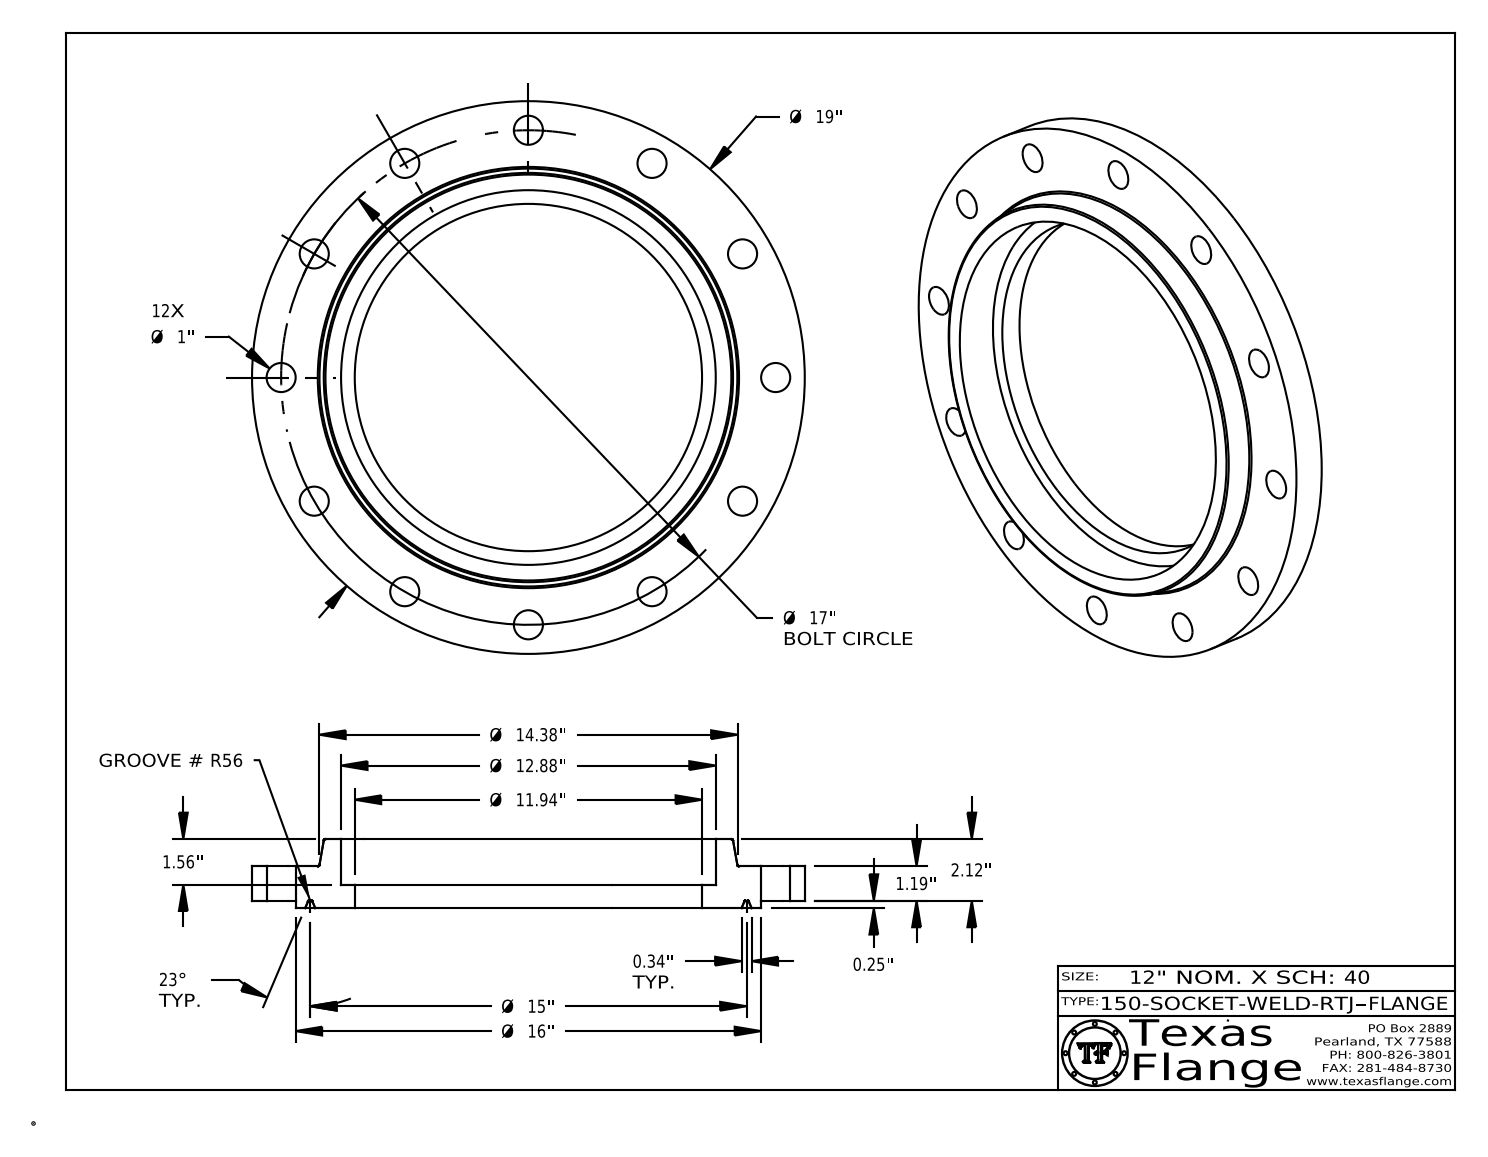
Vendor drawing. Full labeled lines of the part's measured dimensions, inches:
Part name (STEP PRODUCT): 150-SOCKET-WELD-RTJ
STEP written by: CATIA V5 STEP AP214 (AUTOMOTIVE_DESIGN)
Units: inches
Bodies: 1 solid, 438 faces (372 planar, 52 cylindrical, 14 other)
Overall size (bounding box): 19 × 19 × 2.37
Volume: 227.4 in³ · Surface area: 594.9 in²
Round holes (diameter × count): ⌀1 ×12, ⌀0.495 ×1, ⌀11.938 ×1, ⌀12.88 ×1
Round bosses / shafts (diameter × count): ⌀0.03 ×8, ⌀19 ×1, ⌀16 ×1, ⌀0.39 ×1
Main face-to-face distances: 1.19, 0.25, 1.44, 2.37, 2.12, 0.93, 0.81, 0.56, 0.63, 1.56
Hole centre spacings: 8.5, 16.42, 4.4, 12.02, 14.722, 4.4, 12.021, 14.722
